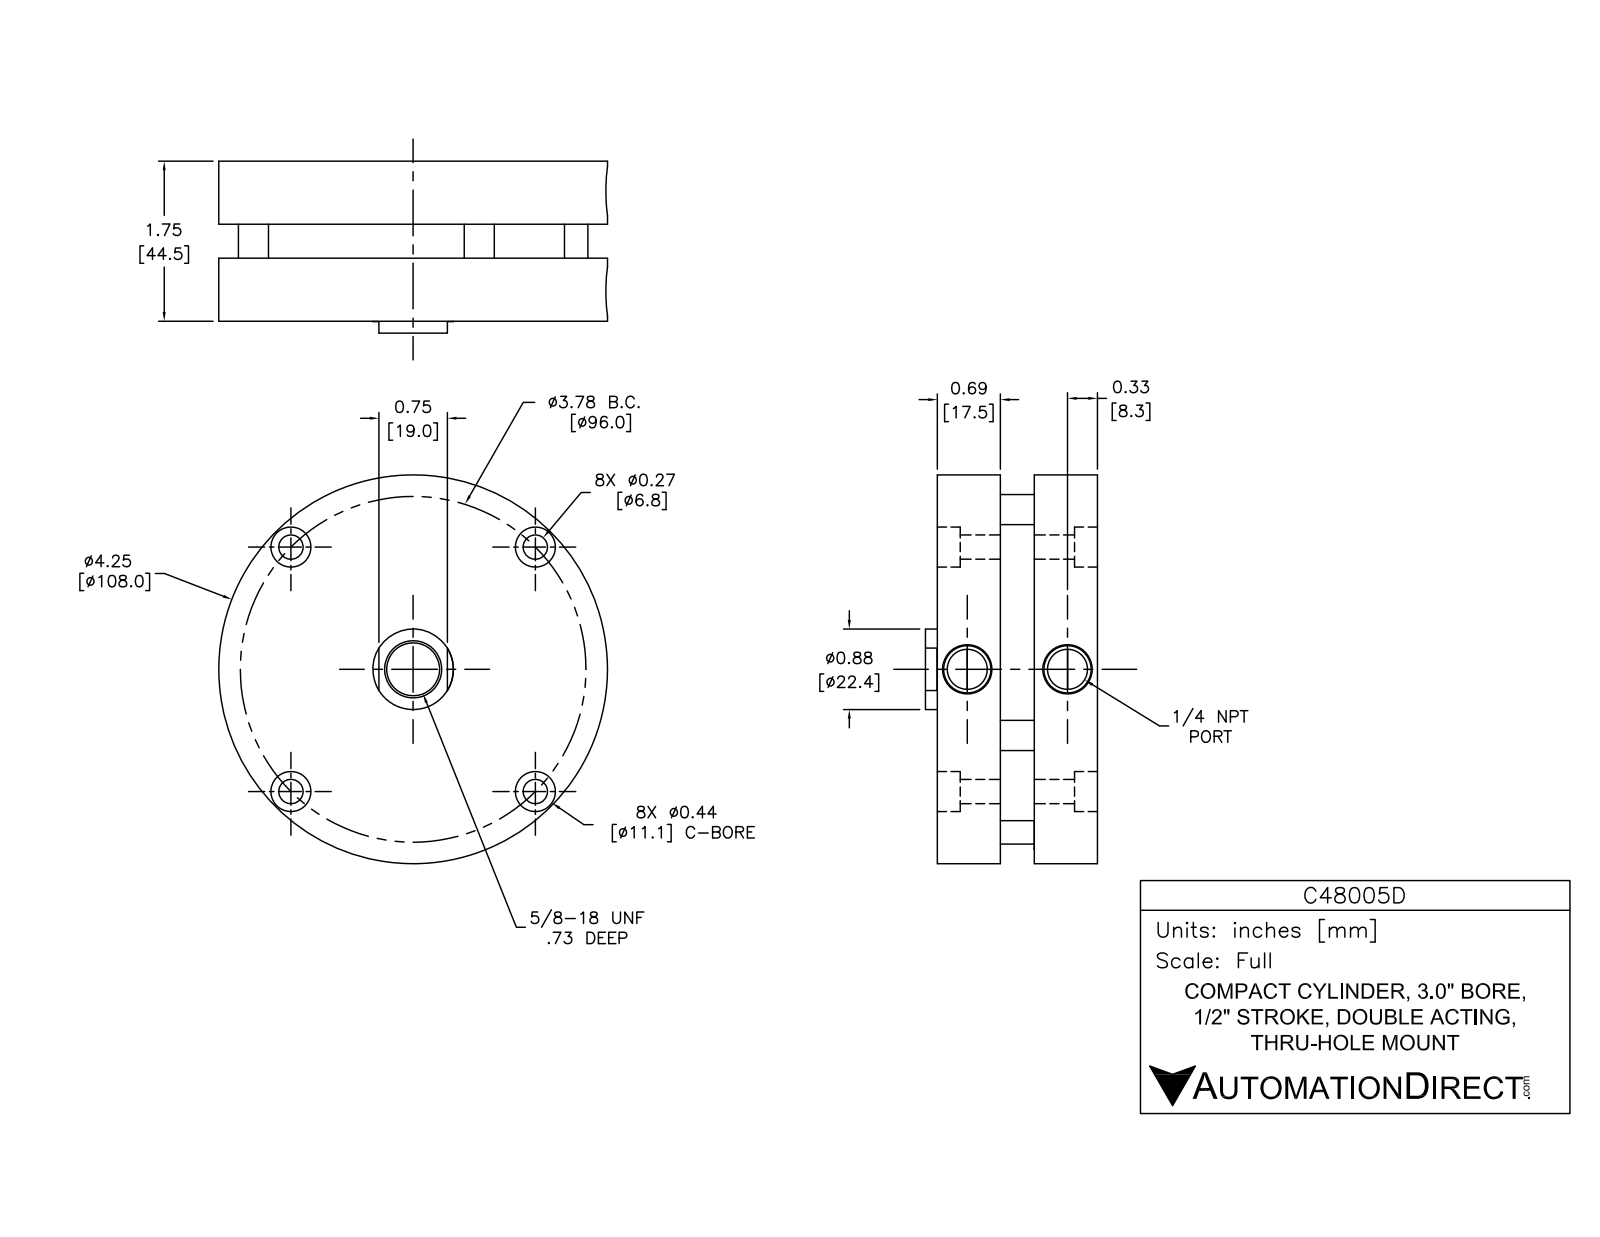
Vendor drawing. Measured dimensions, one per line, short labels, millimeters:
name: C48005D-FO1_BM_rod; C48005D-FO1_BM_r; C48005D-FO1_BM_heads (2); C48005D (+3 more)
written by: SolidWorks 2014 (AUTOMOTIVE_DESIGN)
unit: mm
bodies: 9 solids, 165 faces (49 planar, 98 cylindrical, 18 other)
size: 108 × 108 × 47.8
volume: 305 300 mm³; area: 90 000 mm²
holes: 4× ⌀5.7, 4× ⌀7.1, 4× ⌀10.3, 2× ⌀5.5, 1× ⌀14.4, 1× ⌀22.4, 1× ⌀22.4, 1× ⌀76.2, 1× ⌀79.4
bosses: 4× ⌀11.4, 4× ⌀5.7, 1× ⌀108
face distances: 9.8, 34.7, 17.5, 26.9, 7.8, 17.2, 44.5, 24.9, 9.4, 22
hole spacings: 12.1, 48, 48, 58.8, 67.9, 67.9, 75.9, 95.3
